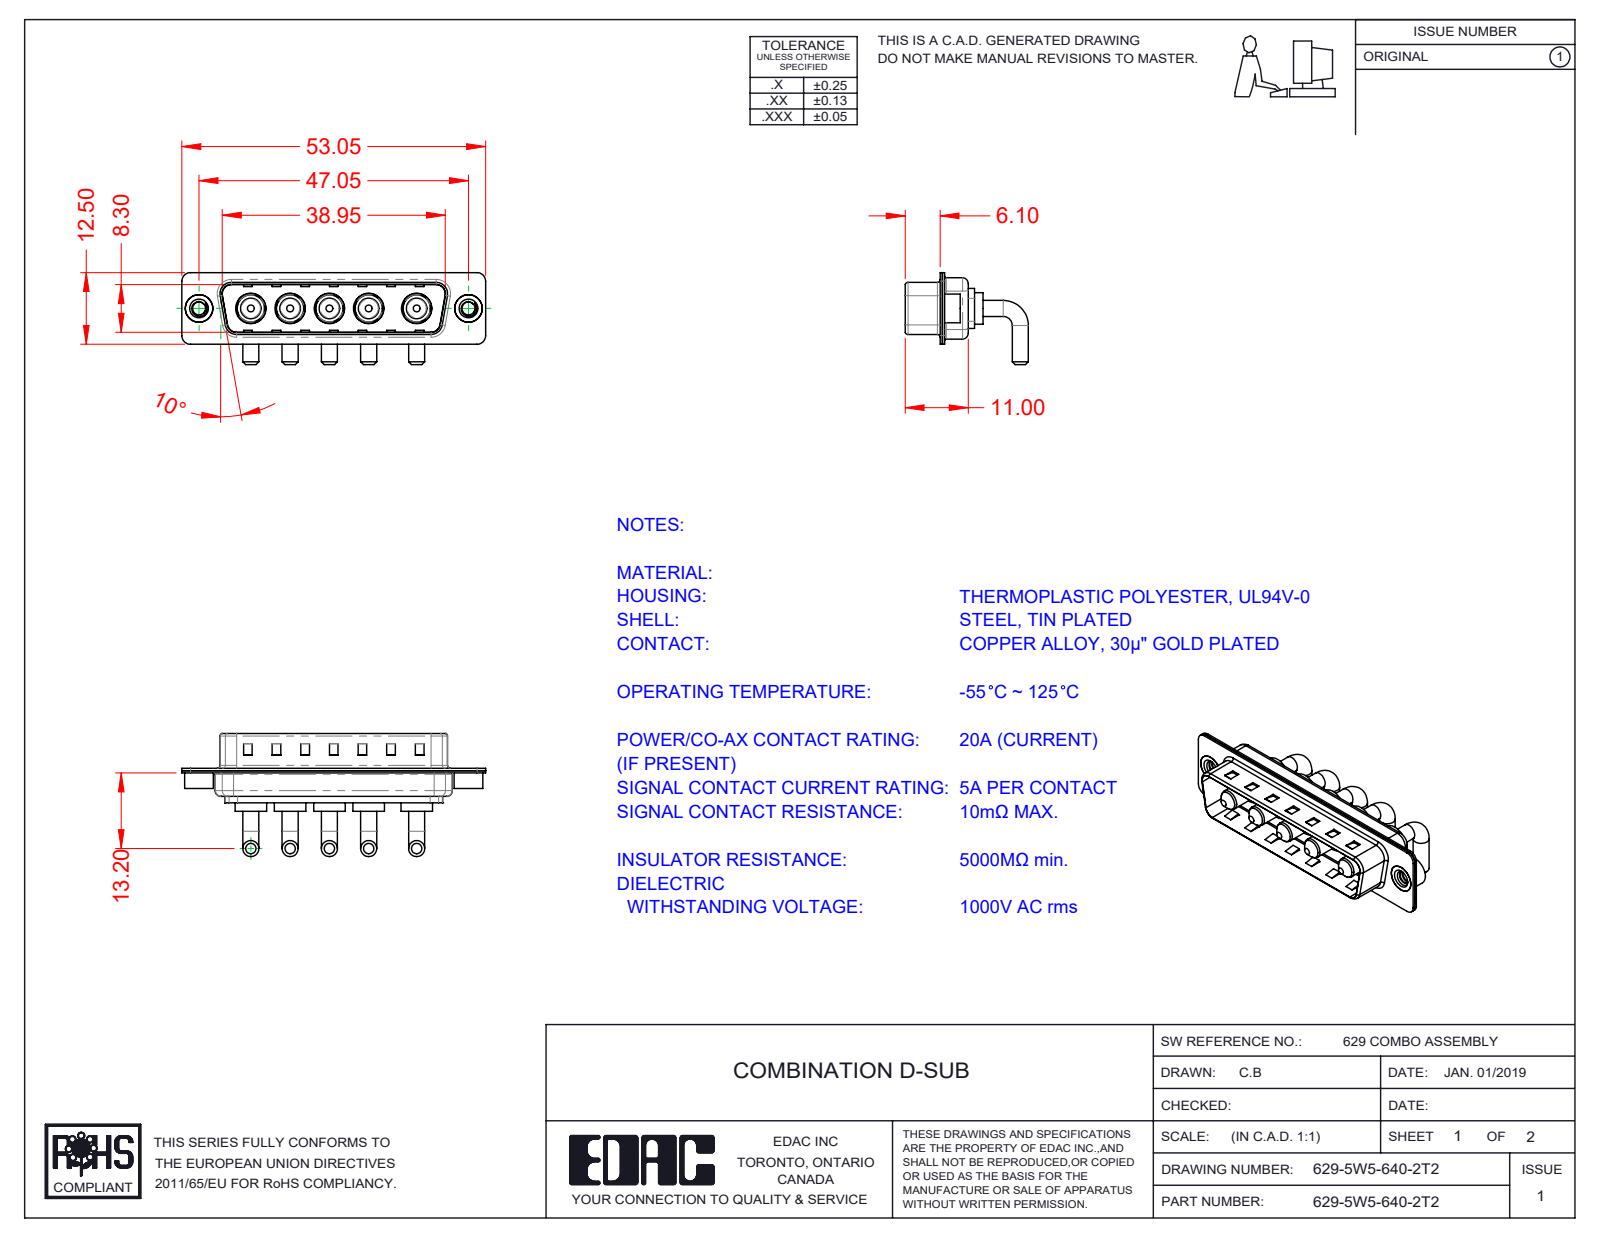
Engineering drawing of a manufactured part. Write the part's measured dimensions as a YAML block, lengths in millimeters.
part_name: "629Combo Housing_5W5; 629Combo Shell Front_25 Contacts; 629-5W5-640-2T2; 629Combo Shell Rear_25 Contacts (+2 more)"
step_written_by: "SolidWorks 2020 (CONFIG_CONTROL_DESIGN)"
units: millimeters
bodies: {solids: 15, faces: 591, planar: 221, cylindrical: 242, other: 128}
overall_size: [53.05, 21.5, 16.05]
volume: 3402
surface_area: 7146
round_holes:
  - {diameter: 4.85, count: 5}
  - {diameter: 5.3, count: 5}
  - {diameter: 2.26, count: 2}
  - {diameter: 4, count: 2}
  - {diameter: 4.8, count: 2}
round_bosses_or_shafts:
  - {diameter: 2.8, count: 10}
  - {diameter: 5.5, count: 5}
  - {diameter: 5.2, count: 5}
  - {diameter: 4.75, count: 5}
  - {diameter: 3.75, count: 5}
  - {diameter: 3.6, count: 5}
  - {diameter: 5, count: 2}
  - {diameter: 4.9, count: 2}
partial_cylinders:
  - {radius: 1.5, count: 16}
  - {radius: 2, count: 12}
  - {radius: 0.5, count: 8}
  - {radius: 1.6, count: 8}
  - {radius: 2.1, count: 5}
  - {radius: 0.25, count: 4}
  - {radius: 0.6, count: 4}
  - {radius: 0.65, count: 4}
face_to_face_distances: [0.4, 0.8, 9.5, 9.1, 8.7, 9.9, 0.75, 1.2, 0.35, 6]
hole_center_spacings: [6.86, 13.73, 6.85, 6.87, 8.37, 8.38, 9.04, 9.05]
